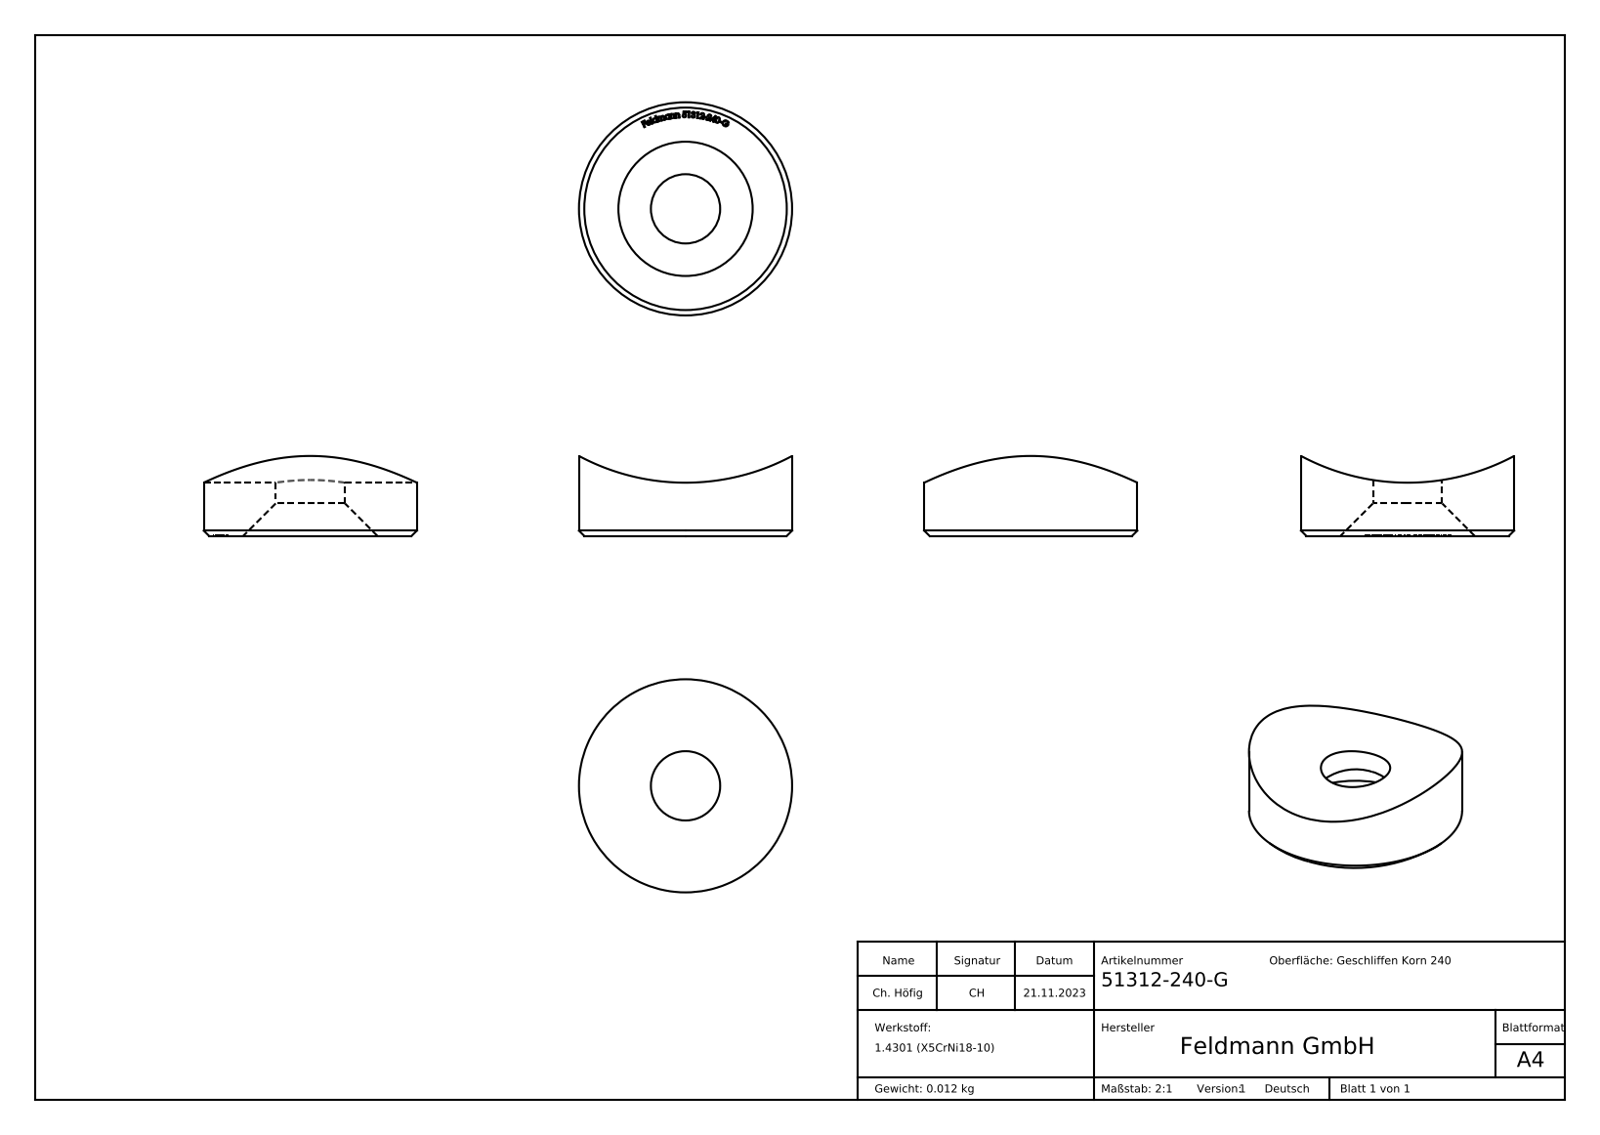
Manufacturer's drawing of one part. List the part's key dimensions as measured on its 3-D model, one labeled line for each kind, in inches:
Part name (STEP PRODUCT): 51312-240-G
STEP written by: SolidWorks 2018 (CONFIG_CONTROL_DESIGN)
Units: inches
Bodies: 1 solid, 242 faces (137 planar, 3 cylindrical, 102 other)
Overall size (bounding box): 0.787 × 0.787 × 0.296
Volume: 0.089 in³ · Surface area: 1.595 in²
Round holes (diameter × count): ⌀0.256 ×1
Round bosses / shafts (diameter × count): ⌀0.787 ×1
Partial cylindrical surfaces — rounded edges, fillets, slot ends (radius × count): R0.835 ×1
Main face-to-face distances: 0.021, 0.013, 0.012, 0.023, 0.015, 0.019, 0.013, 0.021, 0.014
